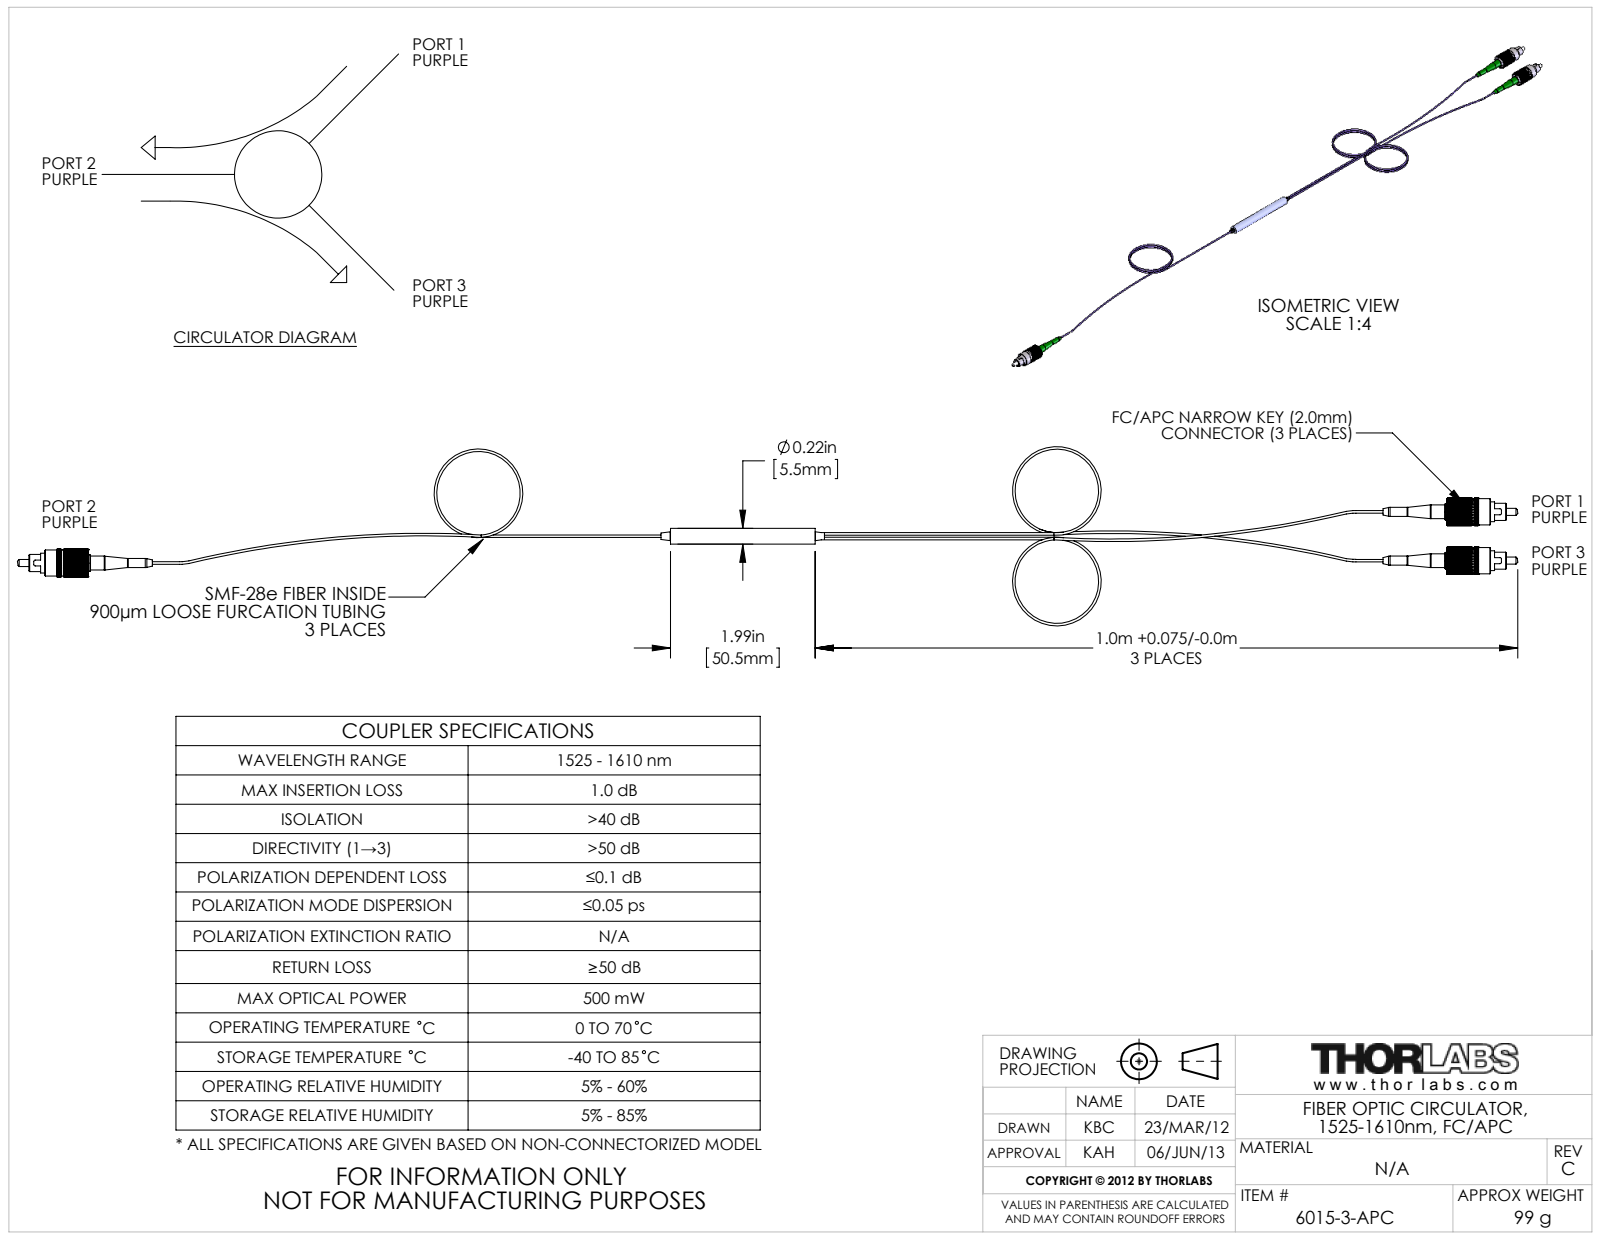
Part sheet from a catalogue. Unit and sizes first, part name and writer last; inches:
Units: inches
Overall size (bounding box): 20.63 × 2.465 × 0.616
Round holes (diameter × count): ⌀0.039 ×3, ⌀0.04 ×3, ⌀0.057 ×3, ⌀0.098 ×3, ⌀0.126 ×3, ⌀0.137 ×3, ⌀0.164 ×3, ⌀0.193 ×3, ⌀0.2 ×3, ⌀0.325 ×2, ⌀0.09 ×1, ⌀0.116 ×1
Round bosses / shafts (diameter × count): ⌀0.36 ×3, ⌀0.313 ×3, ⌀0.273 ×3, ⌀0.229 ×3, ⌀0.19 ×3, ⌀0.125 ×3, ⌀0.035 ×3, ⌀0.035 ×3
Partial cylindrical surfaces — rounded edges, fillets, slot ends (radius × count): R0.02 ×6, R0.12 ×3, R0.19 ×3
Main face-to-face distances: 0.28, 0.281, 0.025, 19.205, 19.18, 0.275, 18.955, 0.25, 18.93, 0.148
Hole centre spacings: 0.033, 0.356, 0.387, 0.065, 0.239, 0.325, 0.325, 0.356
Volume: 0.325 in³ · Surface area: 19.23 in²
Bodies: 15 solids, 1347 faces (737 planar, 468 cylindrical, 142 other)
Part name (STEP PRODUCT): 2394-E0W
STEP written by: SolidWorks 2012 (CONFIG_CONTROL_DESIGN)
